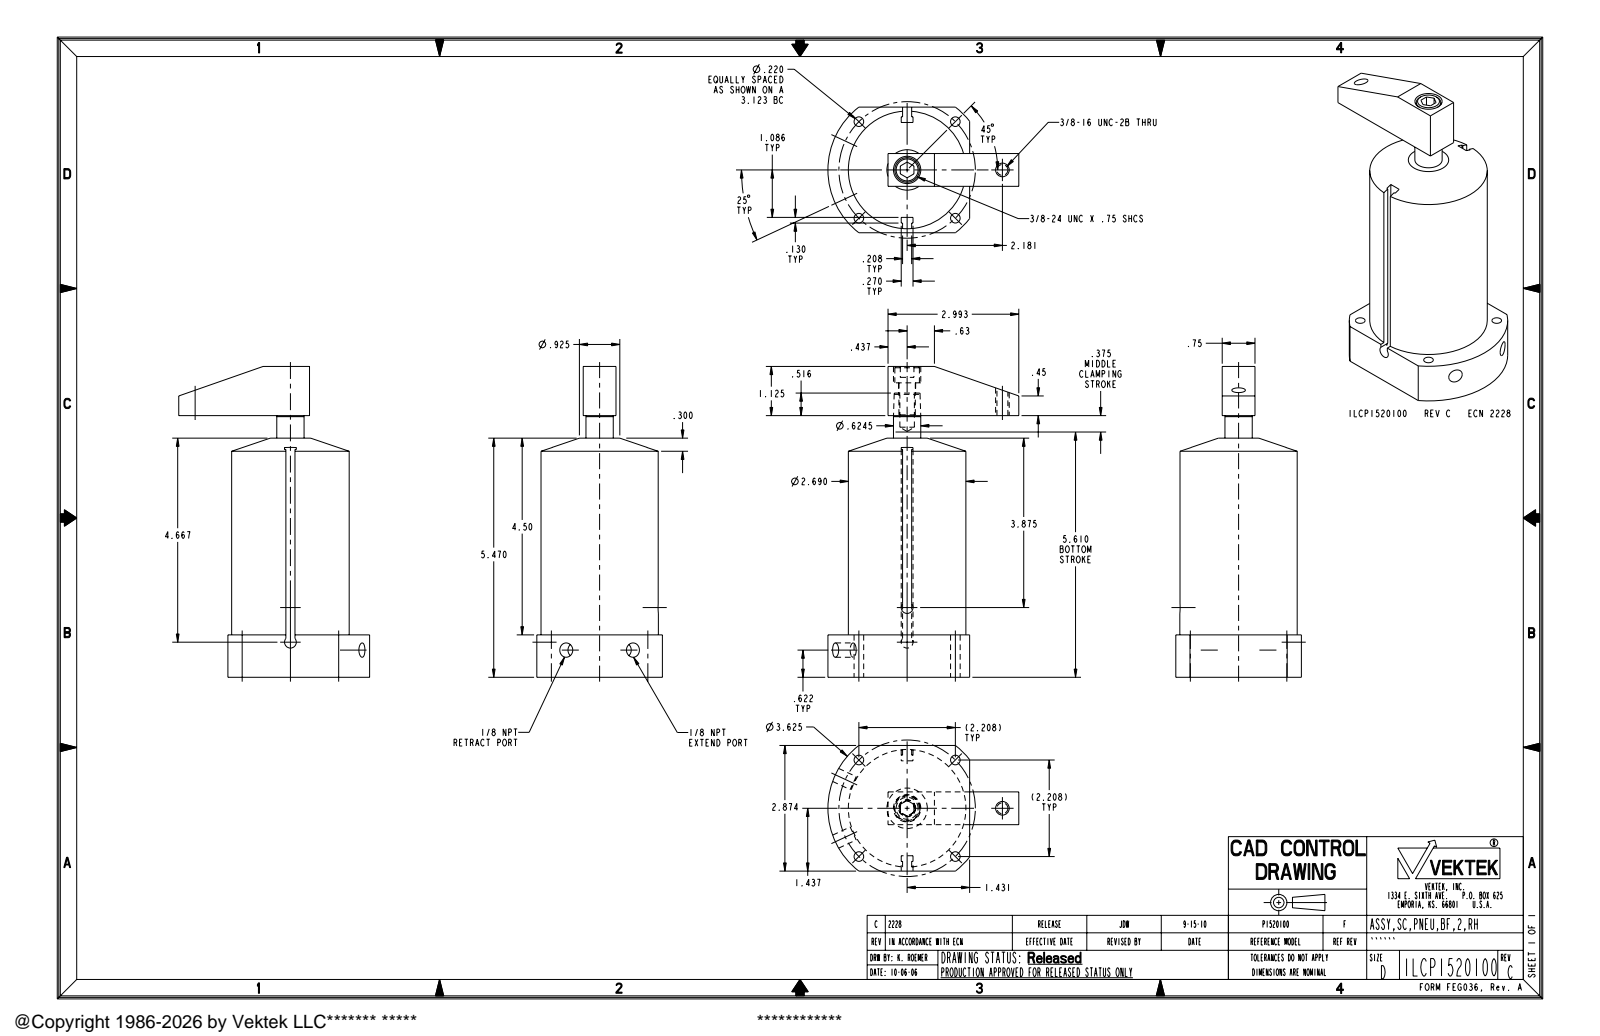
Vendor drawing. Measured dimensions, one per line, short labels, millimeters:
name: ILCP1520100; ILC91501503; ILCP1520100_ASM
written by: PRO/ENGINEER BY PARAMETRIC TECHNOLOGY CORPORATION, 2007460 (AUTOMOTIVE_DESIGN_CC2)
unit: mm
bodies: 2 solids, 91 faces (43 planar, 36 cylindrical, 12 other)
size: 180.6 × 111 × 73
volume: 562 700 mm³; area: 58 610 mm²
holes: 4× ⌀5.6, 2× ⌀8.3, 1× ⌀7.9, 1× ⌀8.4, 1× ⌀9.9, 1× ⌀15.9
bosses: 1× ⌀68.3, 1× ⌀15.8, 1× ⌀14.3, 1× ⌀9.5, 1× ⌀6.4
rounds: 2× R3.4, 1× R46
face distances: 27, 46, 24.6, 19.1, 8.9, 64.1, 18.1, 37.1, 0.8, 73
hole spacings: 39.7, 56.1, 39.2, 79.3, 88, 55.4
